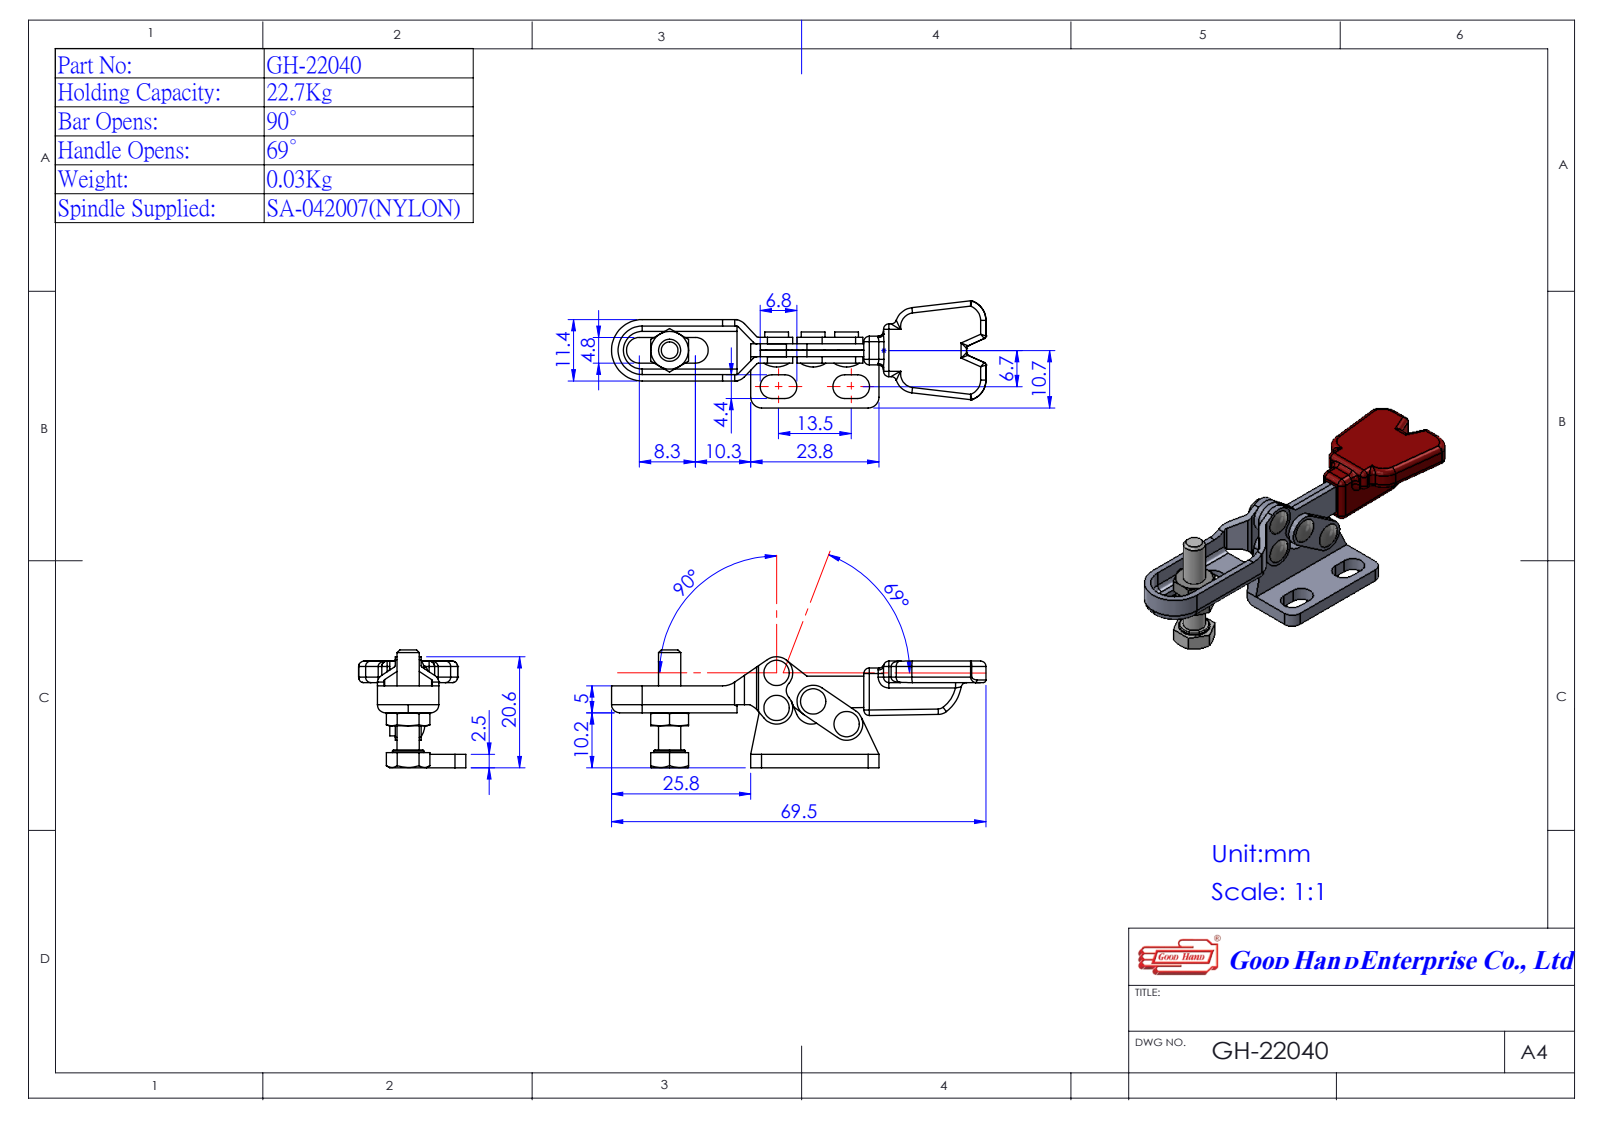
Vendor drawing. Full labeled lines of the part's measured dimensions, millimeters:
Part name (STEP PRODUCT): Group5^GH-22040(簡化); Group3^GH-22040(簡化); 12202013(簡化); 12200501-1^GH-22040(簡化) (+2 more)
STEP written by: SolidWorks 2016 (AUTOMOTIVE_DESIGN)
Units: millimetres
Bodies: 5 solids, 278 faces (117 planar, 113 cylindrical, 48 other)
Overall size (bounding box): 69.5 × 23.3 × 19.89
Volume: 4 504 mm³ · Surface area: 5 283 mm²
Round holes (diameter × count): ⌀2 ×4
Round bosses / shafts (diameter × count): ⌀3.5 ×4, ⌀6 ×1, ⌀5.8 ×1, ⌀4.1 ×1
Partial cylindrical surfaces — rounded edges, fillets, slot ends (radius × count): R1 ×20, R0.5 ×5, R3 ×5, R2 ×4, R2.2 ×4, R2.5 ×3, R2.38 ×2, R3.5 ×2
Main face-to-face distances: 1.2, 2.4, 10.2, 4.5, 6.9, 3.3, 5.7, 19.8, 8.4, 11.4
Hole centre spacings: 6.5, 6.91, 7.49, 8.62, 13.34, 16.1
